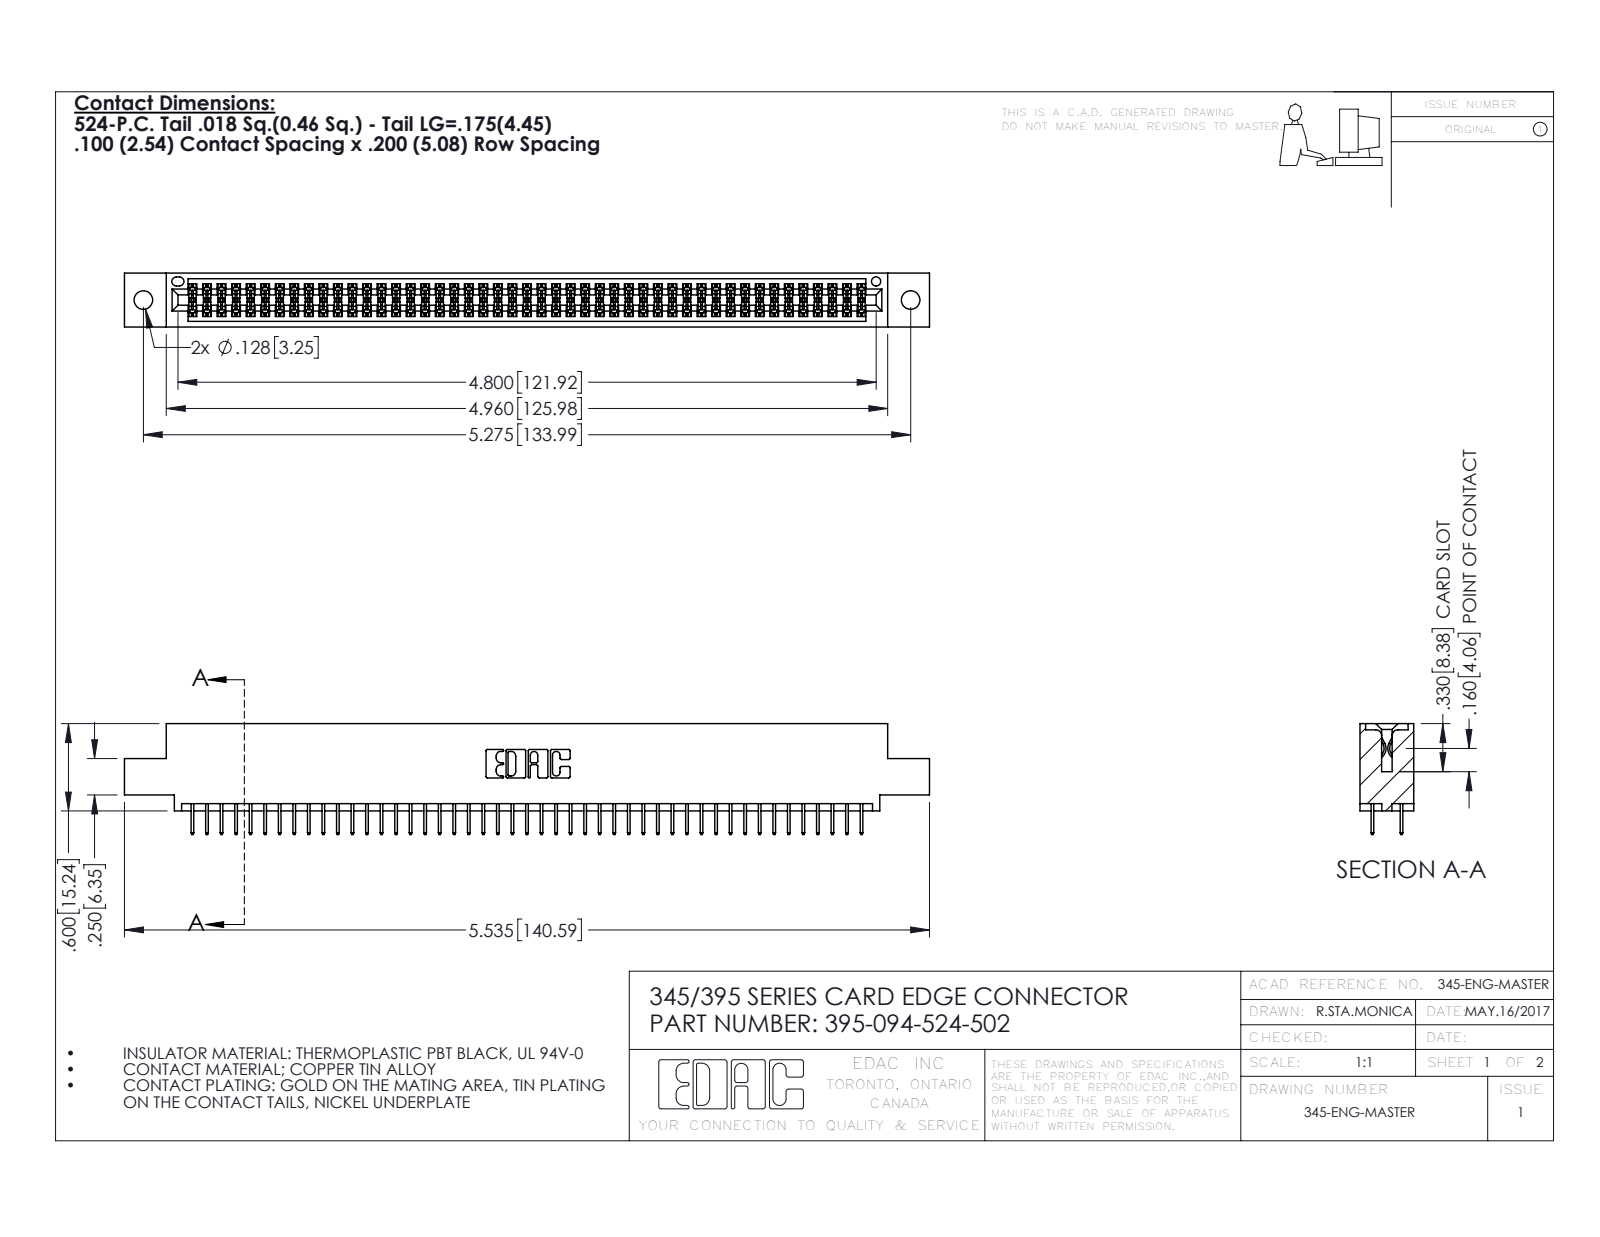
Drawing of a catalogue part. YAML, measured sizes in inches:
part_name: "345 Part_0.110 Offset - 0.128 Dia; 345-292-001_345-293-124; 395-094-524-502"
step_written_by: "SolidWorks 2016 (CONFIG_CONTROL_DESIGN)"
units: inches
bodies: {solids: 95, faces: 5206, planar: 3750, cylindrical: 1456, other: 0}
overall_size: [5.535, 0.762, 0.37]
volume: 0.821
surface_area: 30.11
round_holes:
  - {diameter: 0.128, count: 2}
  - {diameter: 0.064, count: 1}
partial_cylinders:
  - {radius: 0.006, count: 141}
  - {radius: 0.01, count: 22}
  - {radius: 0.007, count: 6}
  - {radius: 0.031, count: 6}
  - {radius: 0.026, count: 3}
  - {radius: 0.014, count: 2}
  - {radius: 0.019, count: 2}
  - {radius: 0.022, count: 2}
face_to_face_distances: [0.072, 0.298, 0.2, 0.37, 0.098, 0.272, 0.025, 0.225, 0.072, 0.175]
hole_center_spacings: [0.27, 5.039, 5.275]
